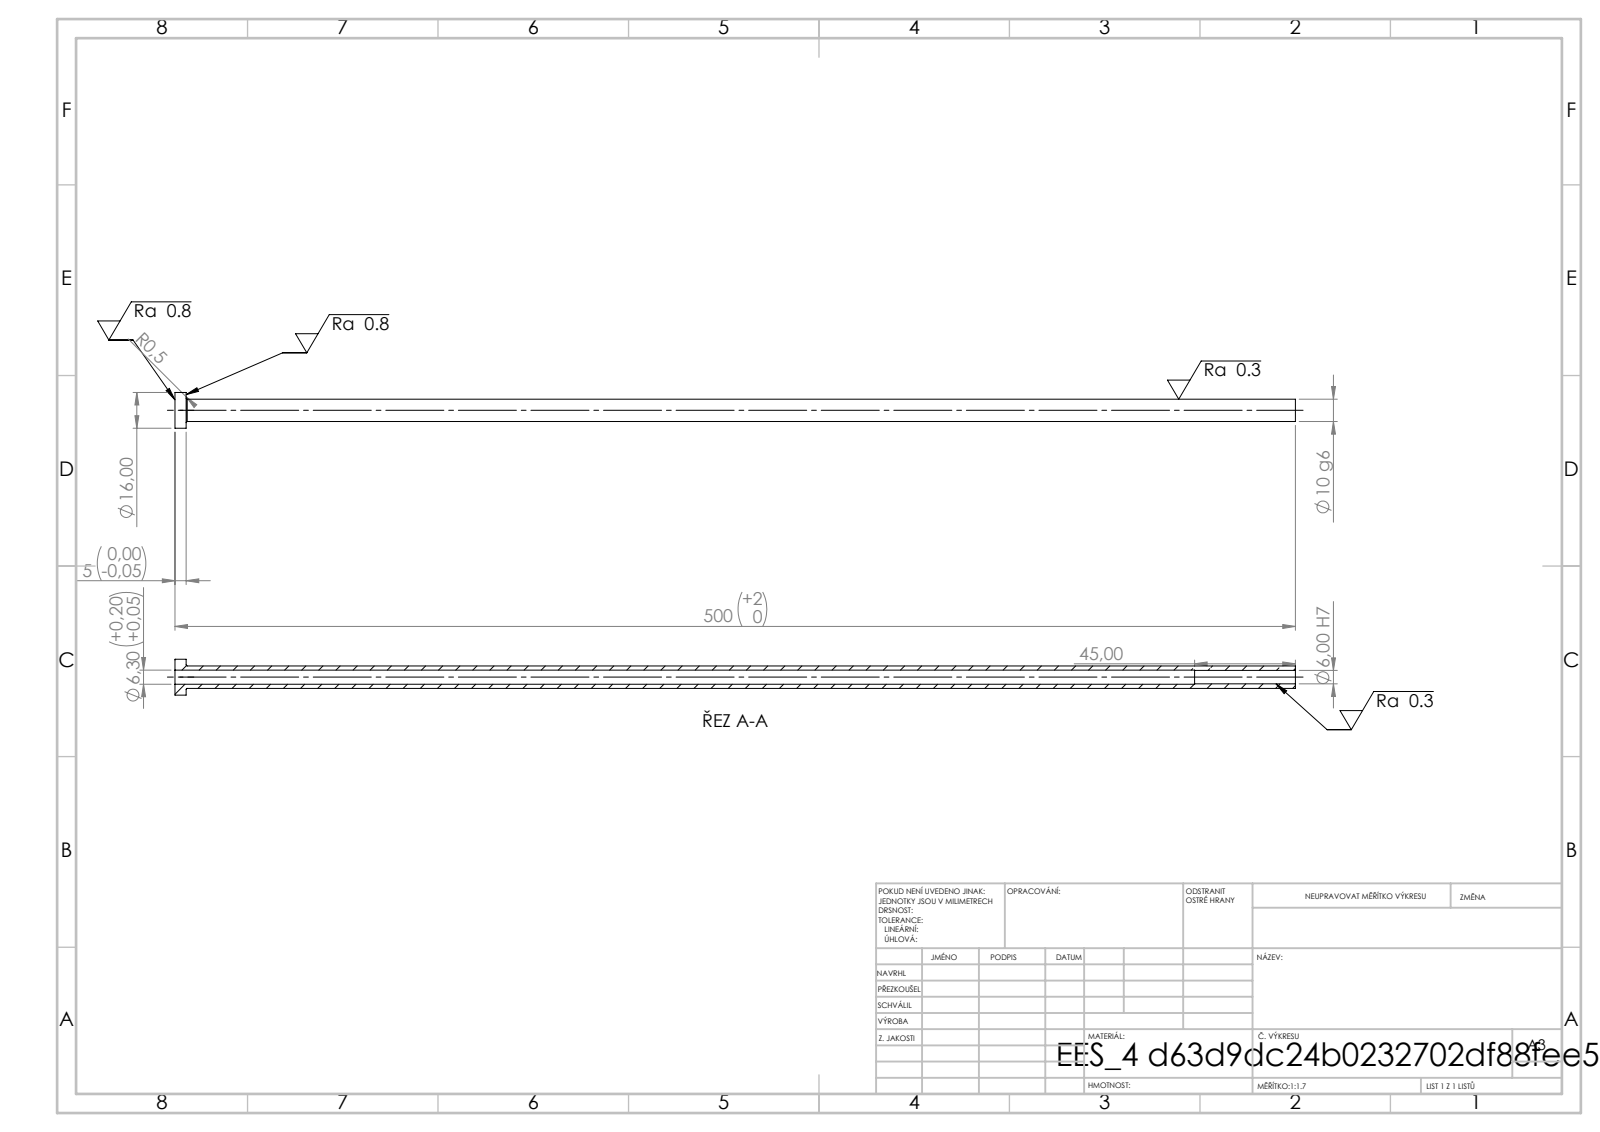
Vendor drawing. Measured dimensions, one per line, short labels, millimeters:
written by: SolidWorks 2019 (CONFIG_CONTROL_DESIGN)
unit: mm
bodies: 1 solid, 14 faces (4 planar, 8 cylindrical, 2 other)
size: 500 × 16 × 16
volume: 24 428 mm³; area: 25 995 mm²
holes: 1× ⌀6, 1× ⌀6.3
bosses: 1× ⌀16, 1× ⌀10
face distances: 5, 500, 495, 455, 450, 45
